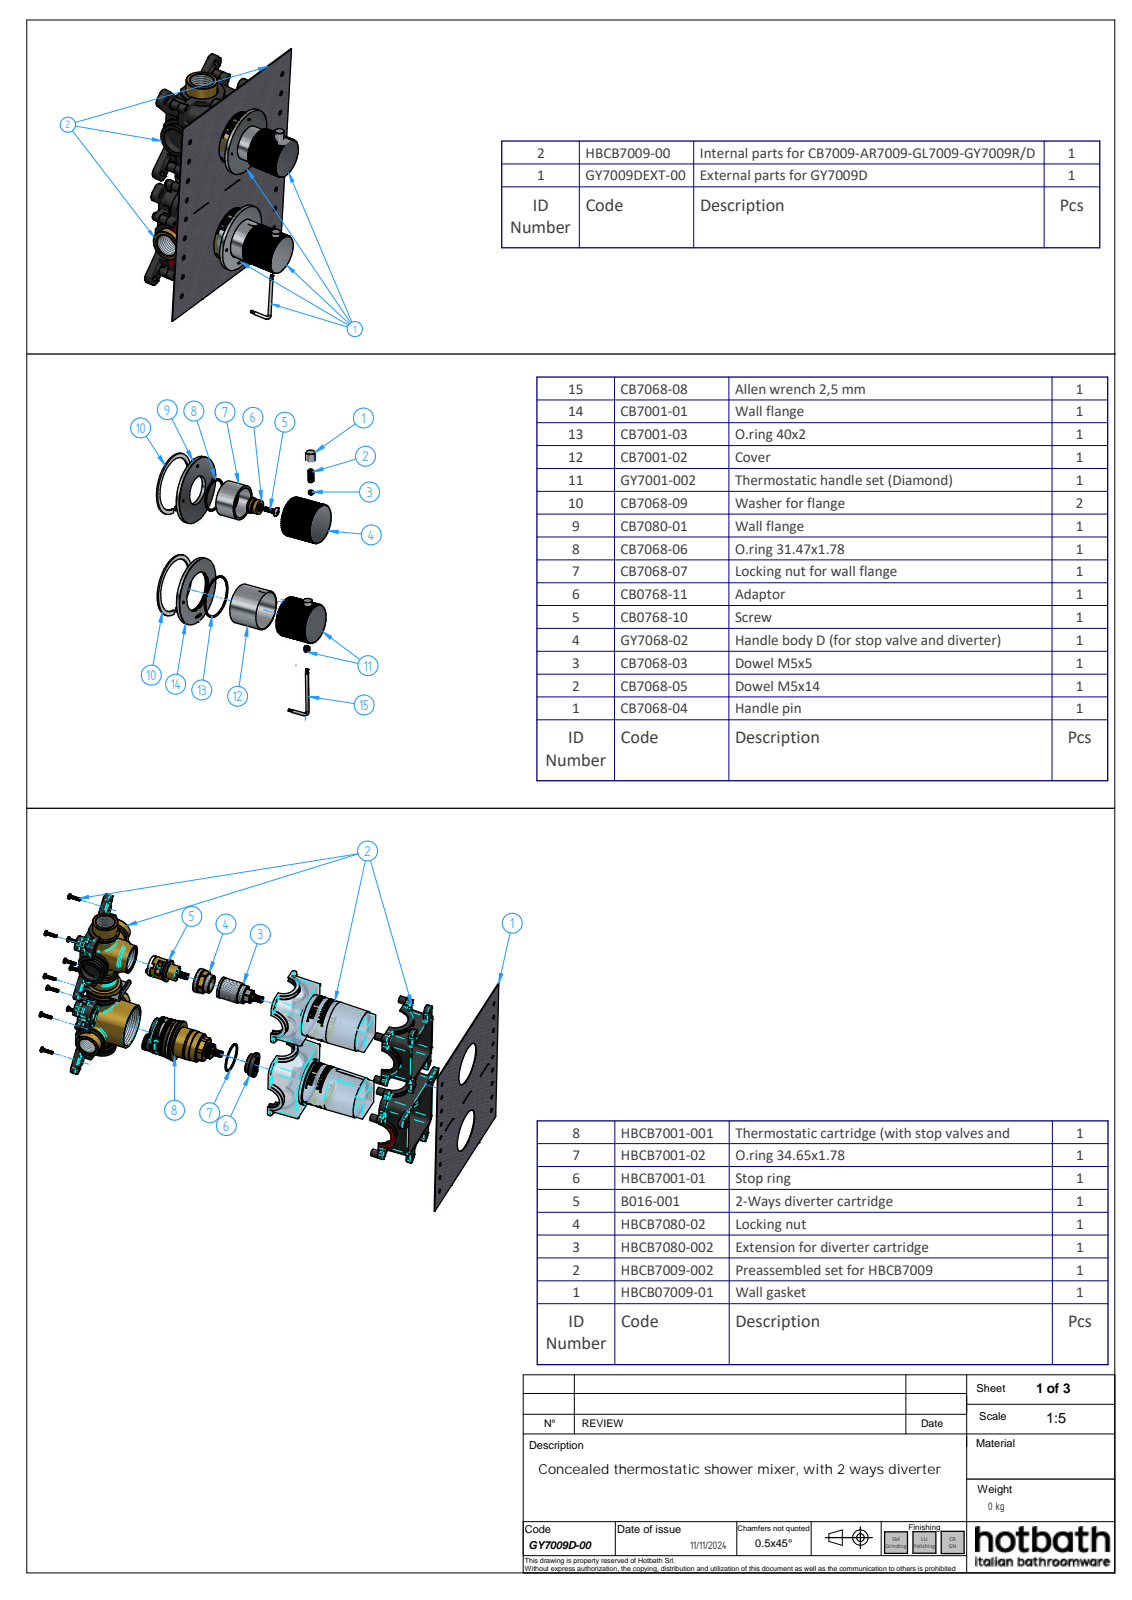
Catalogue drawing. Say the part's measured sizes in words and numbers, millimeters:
The part is named "GY7009D-00; GY7009DEXT-00_oa_0; CB7001-02; CB7001-01 (+8 more)". Its 3-D file was written by "Solid Edge (AUTOMOTIVE_DESIGN)". It is 19 solids with 8853 faces: 3569 planar, 1772 cylindrical and 3512 other. Overall it measures 192 by 72 by 68.3 millimeters. Its volume is 70 755 cubic millimeters and its surface area 66 114 square millimeters. Round holes: 2 of diameter 4.13, 2 of diameter 5.2, 2 of diameter 38, 2 of diameter 57, 2 of diameter 67, 1 of diameter 2, 1 of diameter 2.46, 1 of diameter 3.2, 1 of diameter 4, 1 of diameter 4.5, 1 of diameter 7, 1 of diameter 10.2. Round bosses or shafts: 2 of diameter 72, 2 of diameter 66, 2 of diameter 10, 2 of diameter 5, 2 of diameter 4, 1 of diameter 42, 1 of diameter 17, 1 of diameter 15.15. Partial cylindrical surfaces (rounded edges, fillets, slot ends): 8 of radius 4.5, 2 of radius 0.2, 2 of radius 0.56, 2 of radius 0.73, 2 of radius 1, 2 of radius 2.1, 2 of radius 9.5, 1 of radius 0.49. The main face-to-face distances are 4, 3, 1, 1.5, 4.5, 0.5, 55.43, 55.53, 54.93, 55.03. The hole center spacings are 2, 2.1, 12.5, 14.9, 105.1, 117.6, 120, 132.5.
